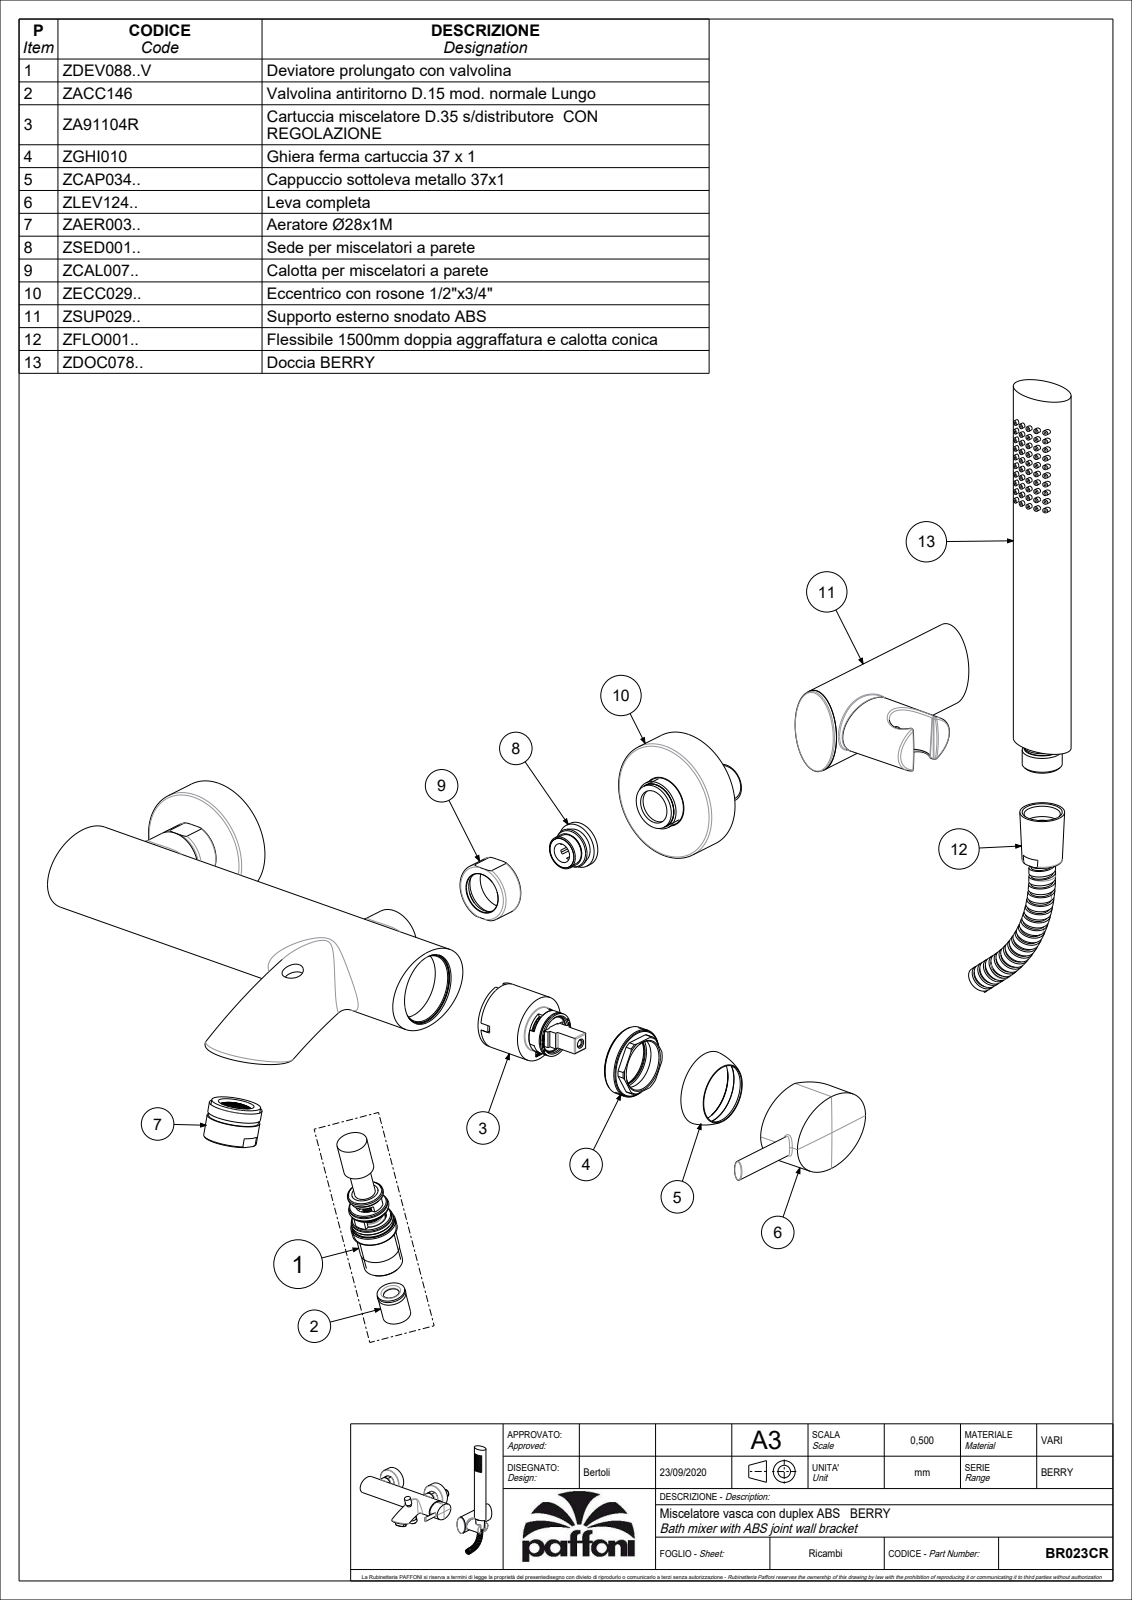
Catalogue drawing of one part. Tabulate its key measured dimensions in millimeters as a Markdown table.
| quantity | value |
| --- | --- |
| part name | 3021196TO; 4111012_A; 4111133CR_A; 4111012_C (+8 more) |
| STEP written by | CREO PARAMETRIC BY PTC INC, 2020044 (CONFIG_CONTROL_DESIGN) |
| units | millimeters |
| bodies | 39 solids, 3614 faces (1980 planar, 744 cylindrical, 890 other) |
| overall size | 414.35 × 320.3 × 177.7 |
| volume | 437 468 mm³ |
| surface area | 283 957 mm² |
| round holes (diameter × count) | 1 × 50, 5 × 5, 19 × 4, 18 × 3, 24.5 × 3, 25 × 3, 3 × 2, 3.5 × 2, 7 × 2, 10 × 2, 10.5 × 2, 16.7 × 2 |
| round bosses / shafts (diameter × count) | 2.5 × 50, 24 × 4, 28 × 3, 16.5 × 3, 16 × 3, 63.5 × 2, 31.2 × 2, 27 × 2 |
| partial cylindrical surfaces (radius × count) | 0.3 × 32, 1 × 14, 0.5 × 12, 4 × 9, 0.8 × 6, 1.25 × 4, 0.8 × 2, 2 × 2 |
| main face-to-face distances | 3.5, 39.5, 0.6, 38.9, 36, 35.4, 52.6, 3, 2.5, 2 |
| hole center spacings | 5, 11.18, 7.07, 10, 15.81, 20.62, 15, 25.5 |
